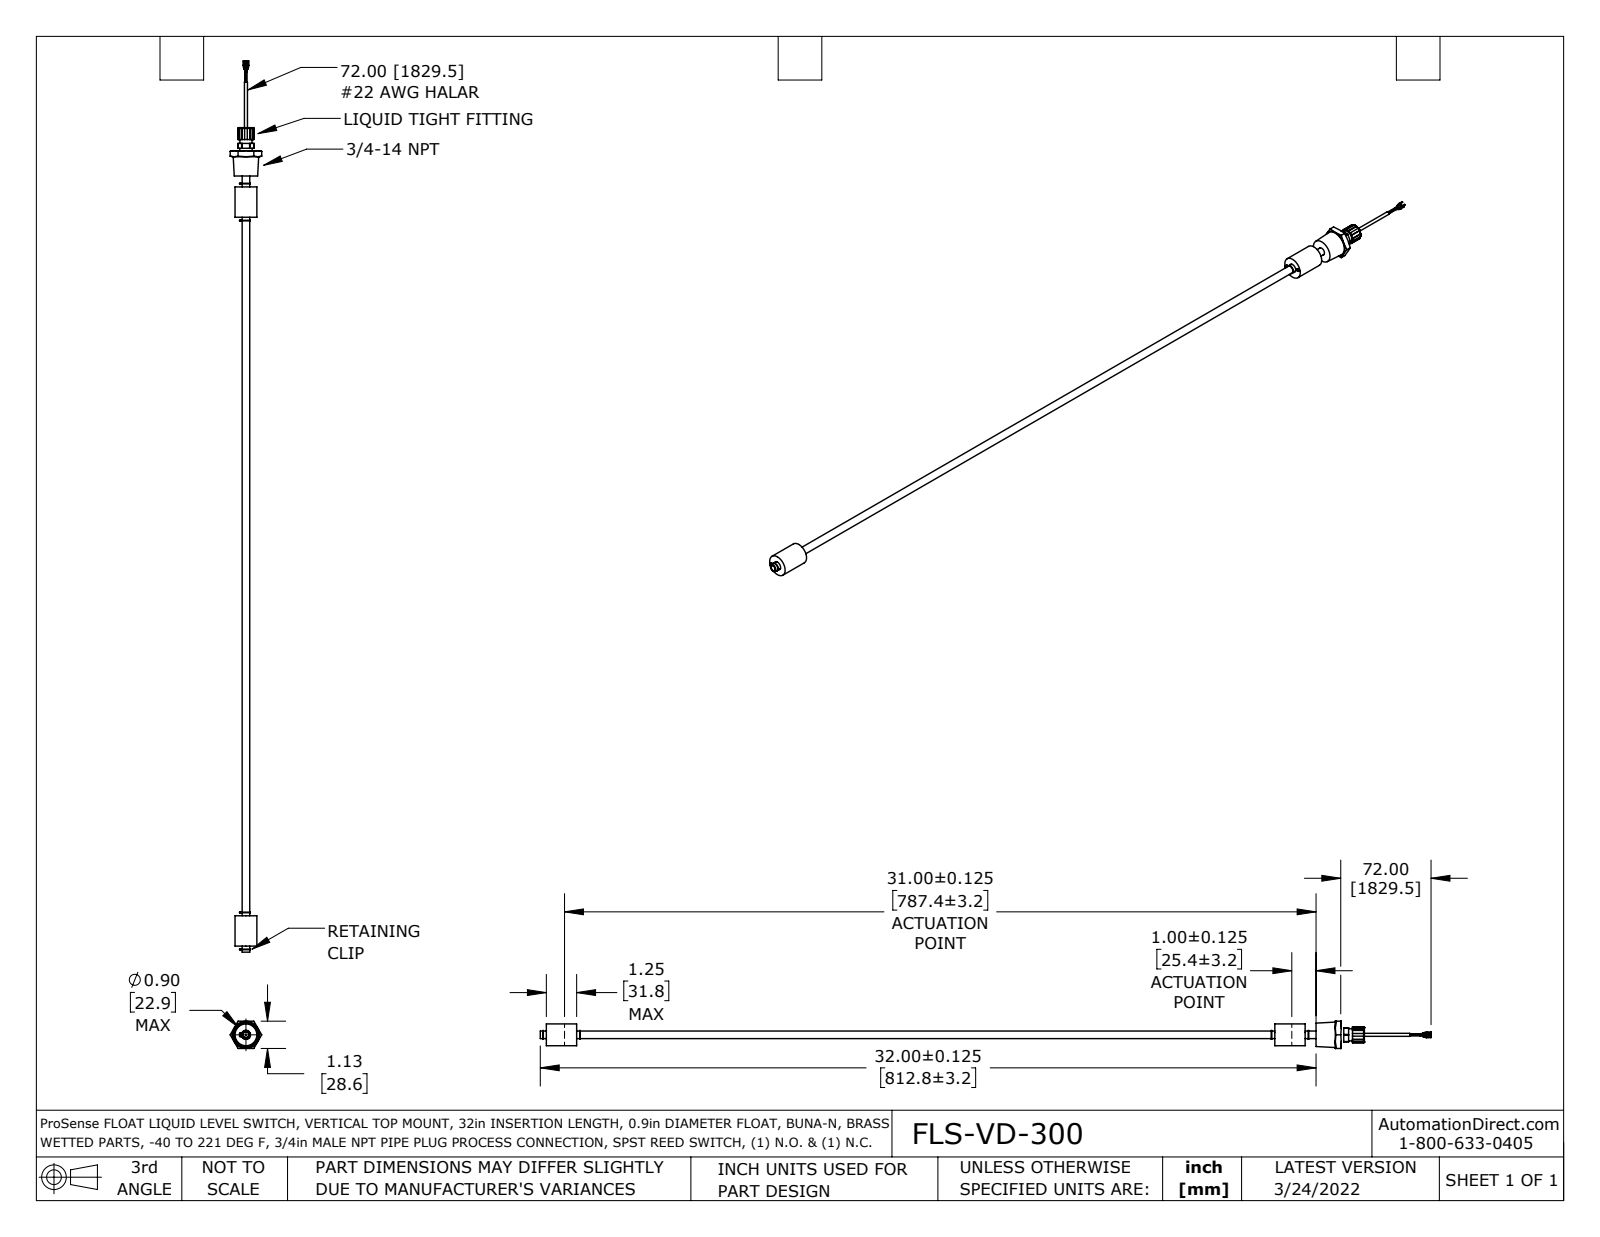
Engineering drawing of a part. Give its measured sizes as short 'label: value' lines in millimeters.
name: ADM4168-3 nc coord fxt
written by: SolidWorks 2021 (AUTOMOTIVE_DESIGN)
unit: mm
bodies: 21 solids, 321 faces (106 planar, 171 cylindrical, 44 other)
size: 933.3 × 33 × 28.6
volume: 54 390 mm³; area: 54 930 mm²
holes: 2× ⌀1, 1× ⌀6.3, 1× ⌀7.1, 1× ⌀7.4, 1× ⌀7.9, 1× ⌀9.5, 1× ⌀9.5
bosses: 12× ⌀0.8, 3× ⌀3.2, 2× ⌀3.2, 1× ⌀22.9, 1× ⌀12.7, 1× ⌀9, 1× ⌀8.4, 1× ⌀8
rounds: 18× R0.8, 2× R0.7, 2× R1.2, 1× R7.6, 1× R8.3
face distances: 31.8, 763.3, 26.5, 832.9, 731.5, 801.2, 774.7, 806.5, 69.7, 43.2
hole spacings: 5.6, 5.7, 2
